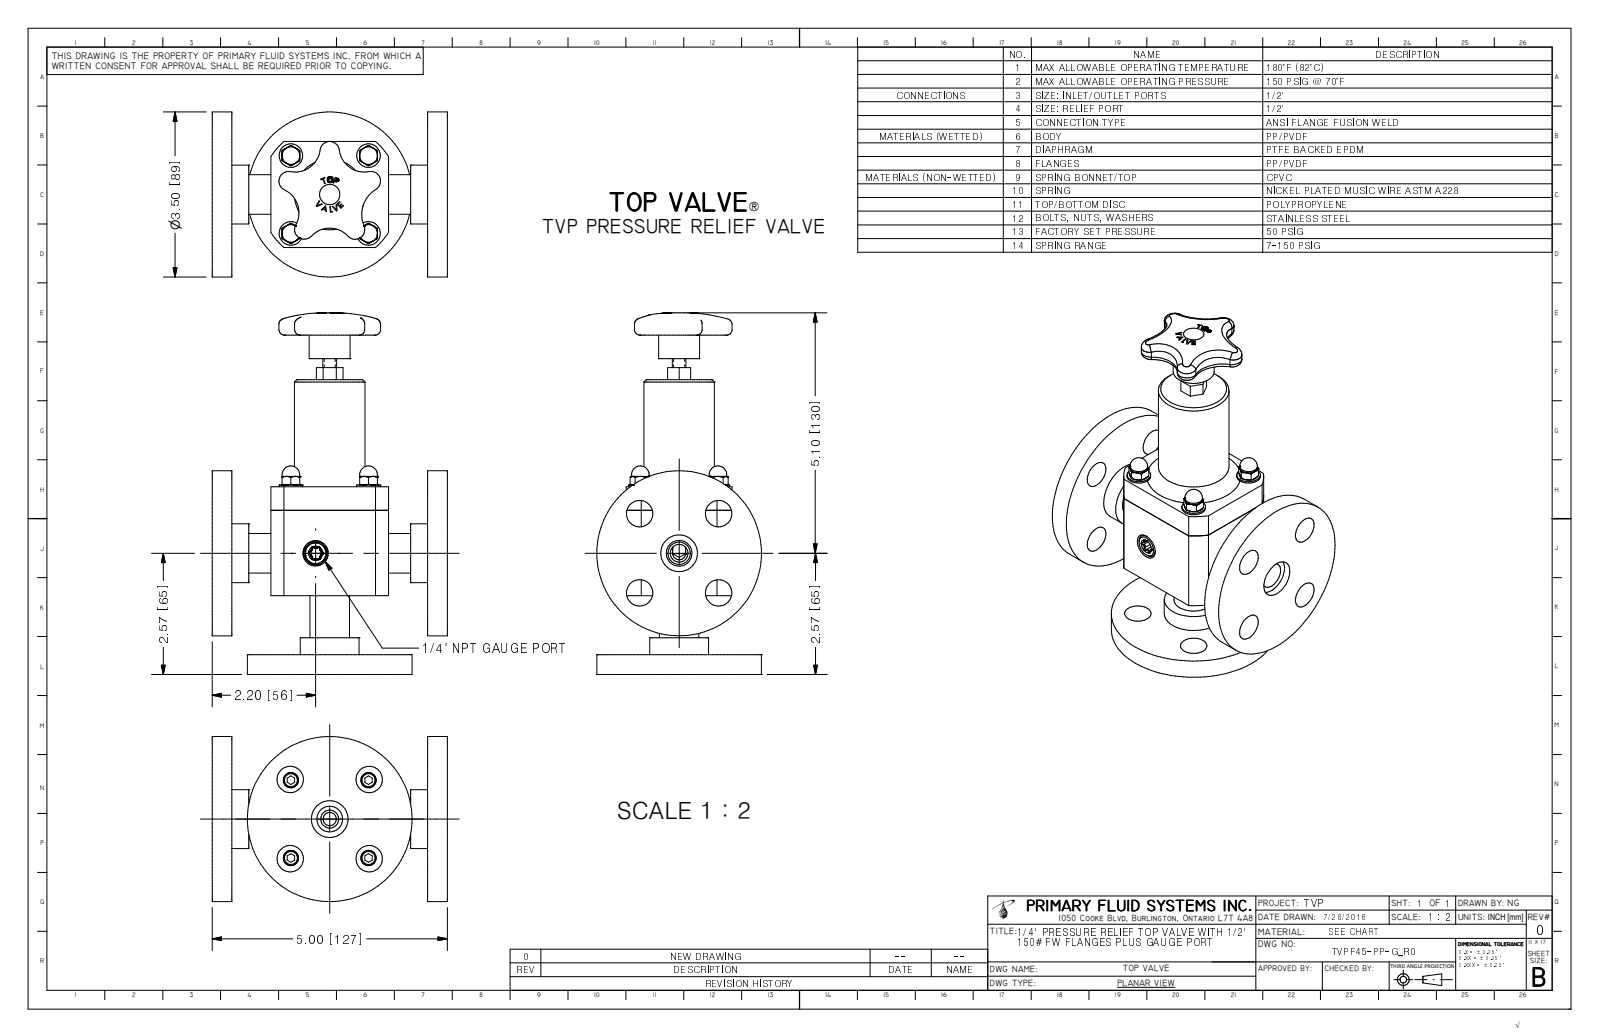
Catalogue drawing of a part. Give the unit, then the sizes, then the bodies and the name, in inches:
Units: inches
Overall size (bounding box): 7.67 × 5 × 3.5
Round holes (diameter × count): ⌀0.56 ×8, ⌀0.147 ×4, ⌀0.546 ×2, ⌀0.78 ×2, ⌀1.525 ×1
Round bosses / shafts (diameter × count): ⌀0.5 ×4, ⌀0.375 ×4, ⌀0.312 ×4, ⌀3.5 ×2, ⌀1.25 ×2, ⌀0.84 ×2, ⌀1.5 ×1, ⌀0.87 ×1
Partial cylindrical surfaces — rounded edges, fillets, slot ends (radius × count): R0.027 ×6, R0.085 ×5, R0.205 ×5, R0.536 ×4, R0.656 ×4, R0.625 ×1, R0.745 ×1, R1.488 ×1
Main face-to-face distances: 0.42, 4.58, 1.25, 5, 4.16, 3.75, 0.83, 3.33, 1.67, 2.25
Hole centre spacings: 1.188, 1.68, 1.665, 2.375, 0.02, 0.021, 1.167, 1.167
Volume: 29.81 in³ · Surface area: 147.3 in²
Bodies: 1 solid, 414 faces (167 planar, 78 cylindrical, 169 other)
Part name (STEP PRODUCT): TVPF45-PP-G_R0
STEP written by: Autodesk Inventor 2009 (AUTOMOTIVE_DESIGN)
